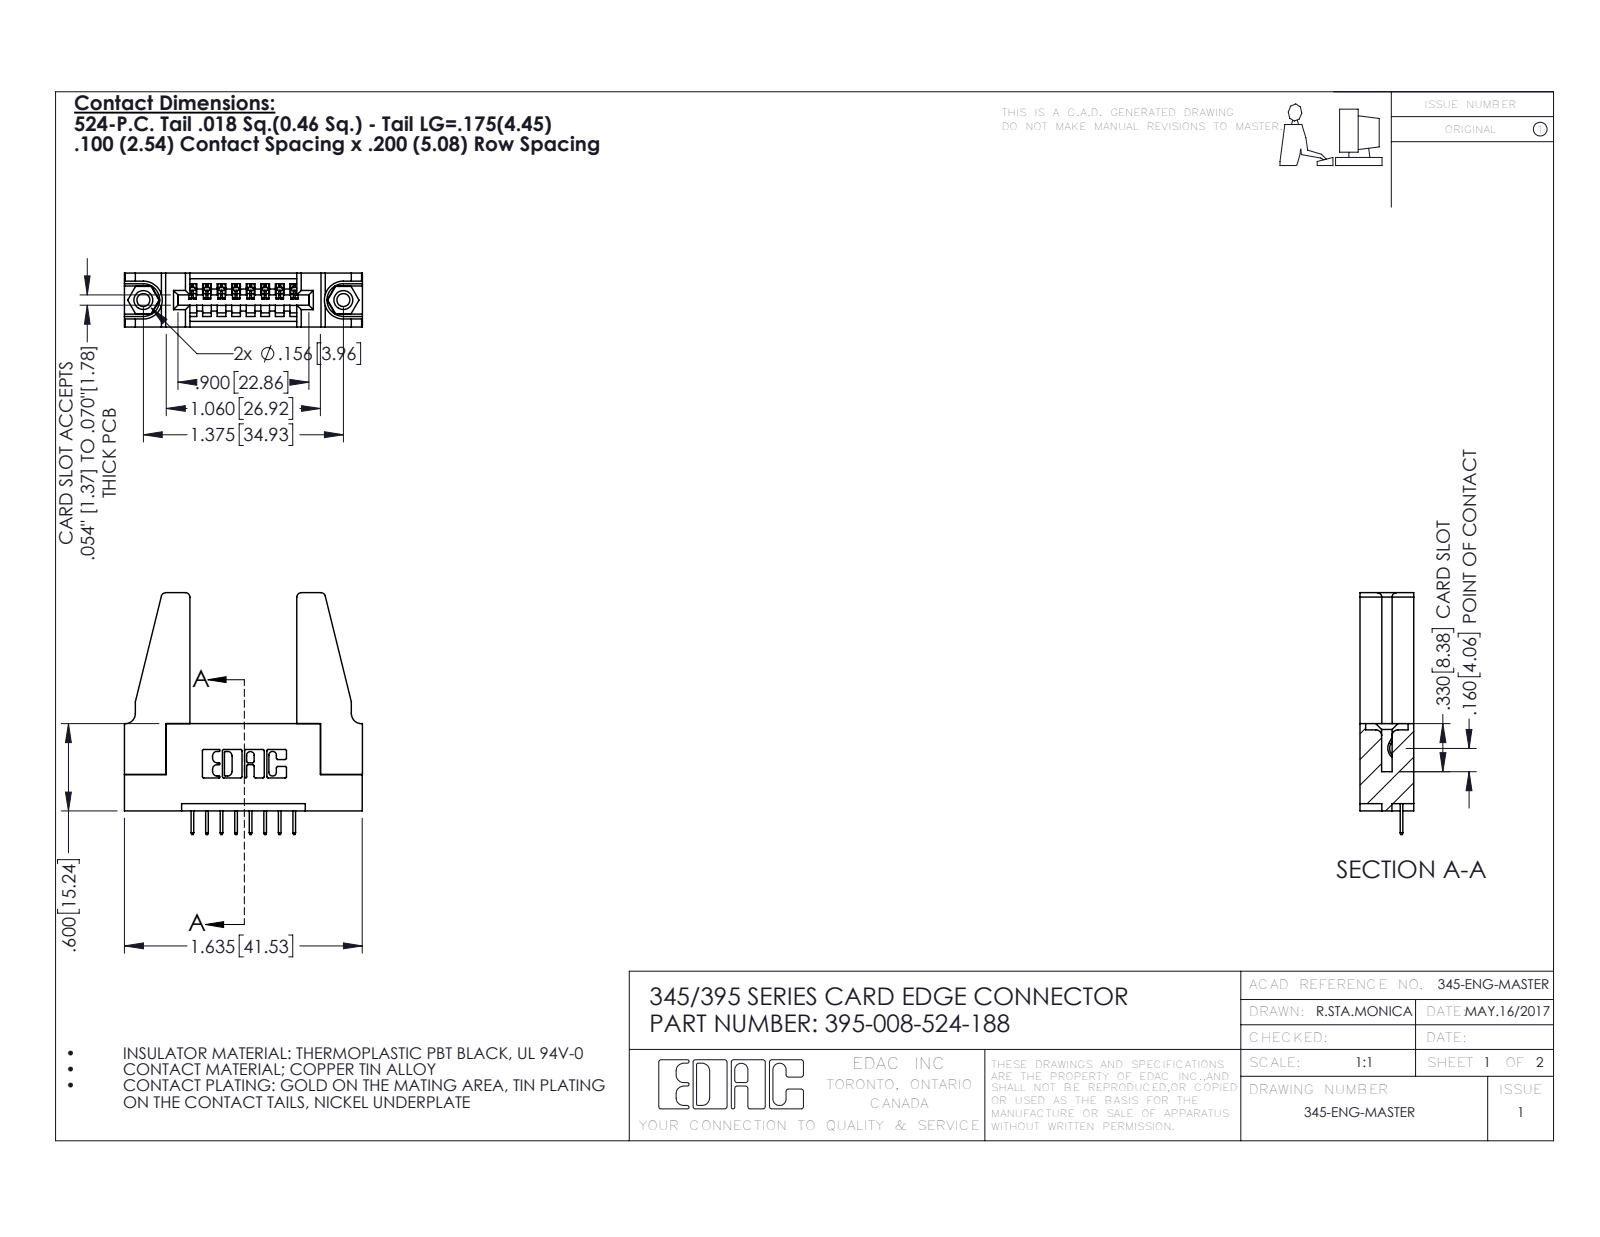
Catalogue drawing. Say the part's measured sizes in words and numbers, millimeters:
The part is named "345-220-078_345-220-088; 345-250-001_345-250-001-102; 395-008-524-188; 345 Part_Flush Mounting Lugs - 0.156 Dia-TH (+1 more)". Its 3-D file was written by "SolidWorks 2016 (CONFIG_CONTROL_DESIGN)". It is 13 solids with 746 faces: 520 planar, 210 cylindrical and 16 other. Overall it measures 42.2 by 41.6 by 9.4 millimeters. Its volume is 6 880 cubic millimeters and its surface area 7 400 square millimeters. Round holes: 2 of diameter 2.3, 2 of diameter 3.2, 2 of diameter 4, 1 of diameter 1.6. Round bosses or shafts: 2 of diameter 3.9. Partial cylindrical surfaces (rounded edges, fillets, slot ends): 22 of radius 0.3, 16 of radius 0.2, 8 of radius 0.8, 6 of radius 0.2, 6 of radius 0.8, 3 of radius 0.7, 2 of radius 0.8, 2 of radius 1. The main face-to-face distances are 9.4, 1.8, 5.1, 7.6, 3.8, 3.8, 8.9, 2.5, 6.9, 0.6. The hole center spacings are 6.9, 29.1, 34.9.
